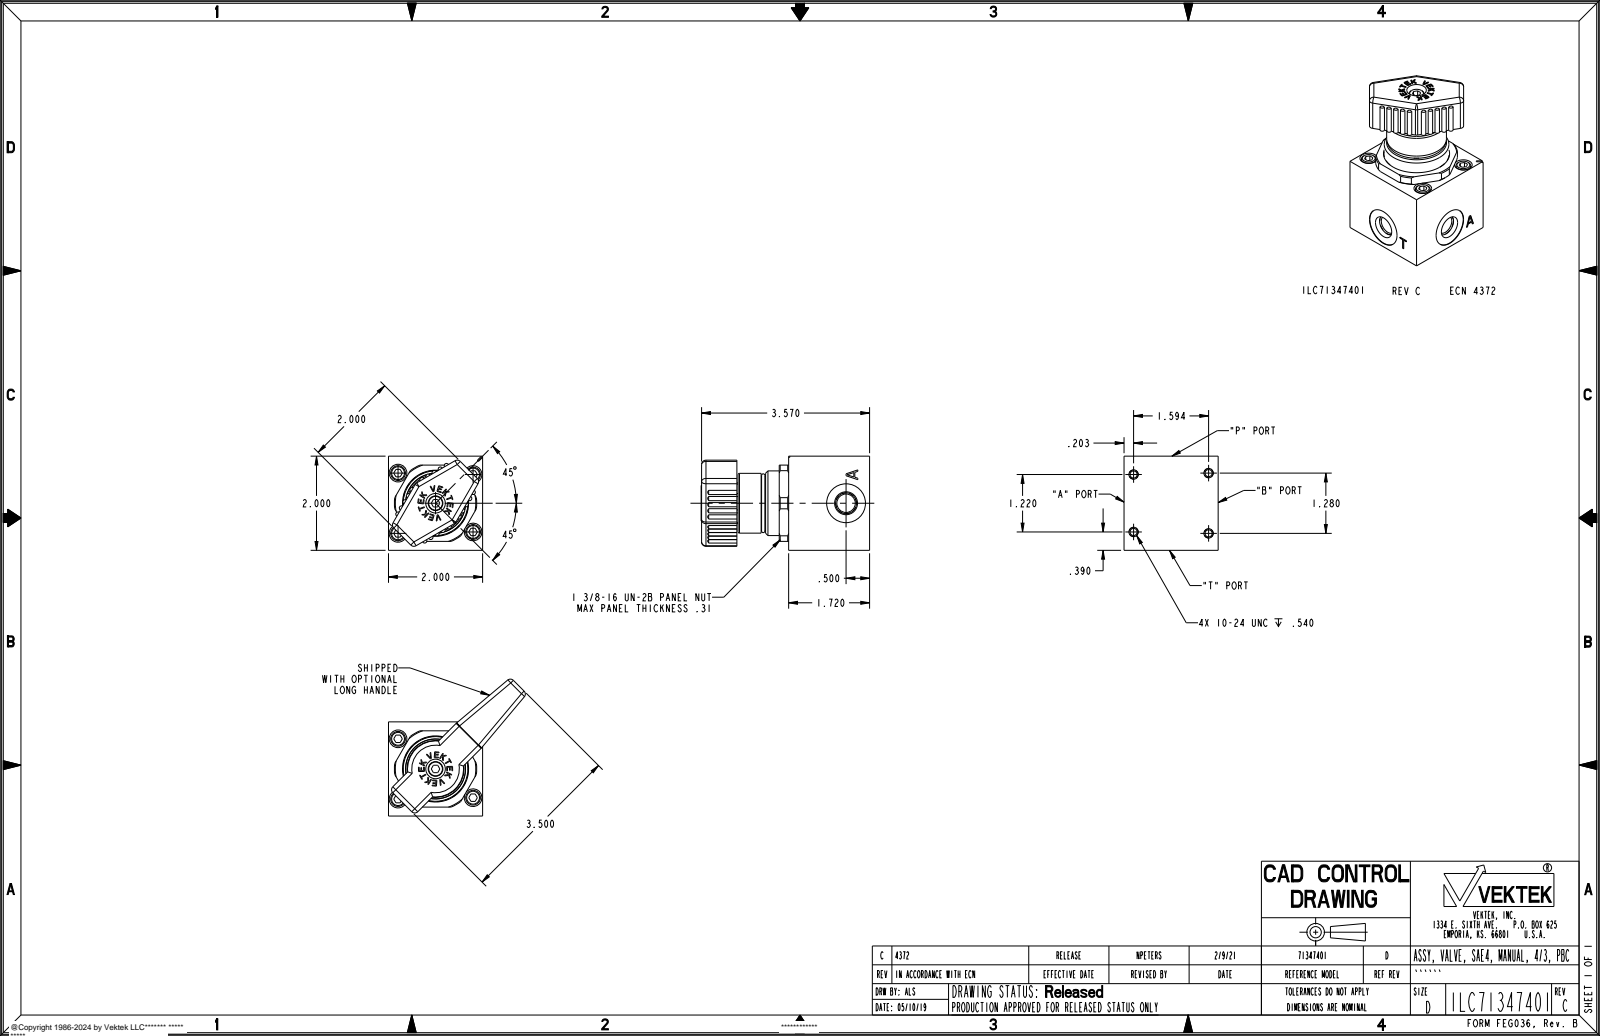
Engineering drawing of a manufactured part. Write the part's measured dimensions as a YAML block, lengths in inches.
part_name: "ILC71347401_BODY; ILC71347401_ADAPTER; 85600903; 87114013 (+2 more)"
step_written_by: "PRO/ENGINEER BY PARAMETRIC TECHNOLOGY CORPORATION, 2013320 (AP203_CONFIGURATION_CONTROLLED_3D_DESIGN_OF_MECHANICAL_PARTS_AND_ASSEMBLIES_MIM_LF)"
units: inches
bodies: {solids: 6, faces: 1734, planar: 1396, cylindrical: 216, other: 122}
overall_size: [3.58, 2.908, 2.908]
volume: 10.12
surface_area: 75.42
round_holes:
  - {diameter: 0.151, count: 4}
  - {diameter: 0.196, count: 4}
  - {diameter: 0.375, count: 4}
  - {diameter: 0.199, count: 2}
  - {diameter: 0.392, count: 2}
  - {diameter: 0.825, count: 2}
  - {diameter: 0.203, count: 1}
  - {diameter: 0.204, count: 1}
  - {diameter: 0.205, count: 1}
  - {diameter: 0.415, count: 1}
  - {diameter: 0.5, count: 1}
  - {diameter: 1.314, count: 1}
round_bosses_or_shafts:
  - {diameter: 0.19, count: 5}
  - {diameter: 0.313, count: 4}
  - {diameter: 0.437, count: 2}
  - {diameter: 1.387, count: 1}
  - {diameter: 1.373, count: 1}
  - {diameter: 1.27, count: 1}
  - {diameter: 0.312, count: 1}
partial_cylinders:
  - {radius: 0.09, count: 23}
  - {radius: 0.048, count: 20}
  - {radius: 0.093, count: 12}
  - {radius: 0.03, count: 10}
  - {radius: 0.045, count: 8}
  - {radius: 0.062, count: 8}
  - {radius: 0.031, count: 6}
  - {radius: 0.12, count: 4}
face_to_face_distances: [2, 1.72, 0.32, 1.1, 2.82, 0.1, 0.75, 1.42, 3.14, 0.53]
hole_center_spacings: [0.437, 1.004, 1.022, 1.594, 2.026, 0.573, 0.589, 0.874]
